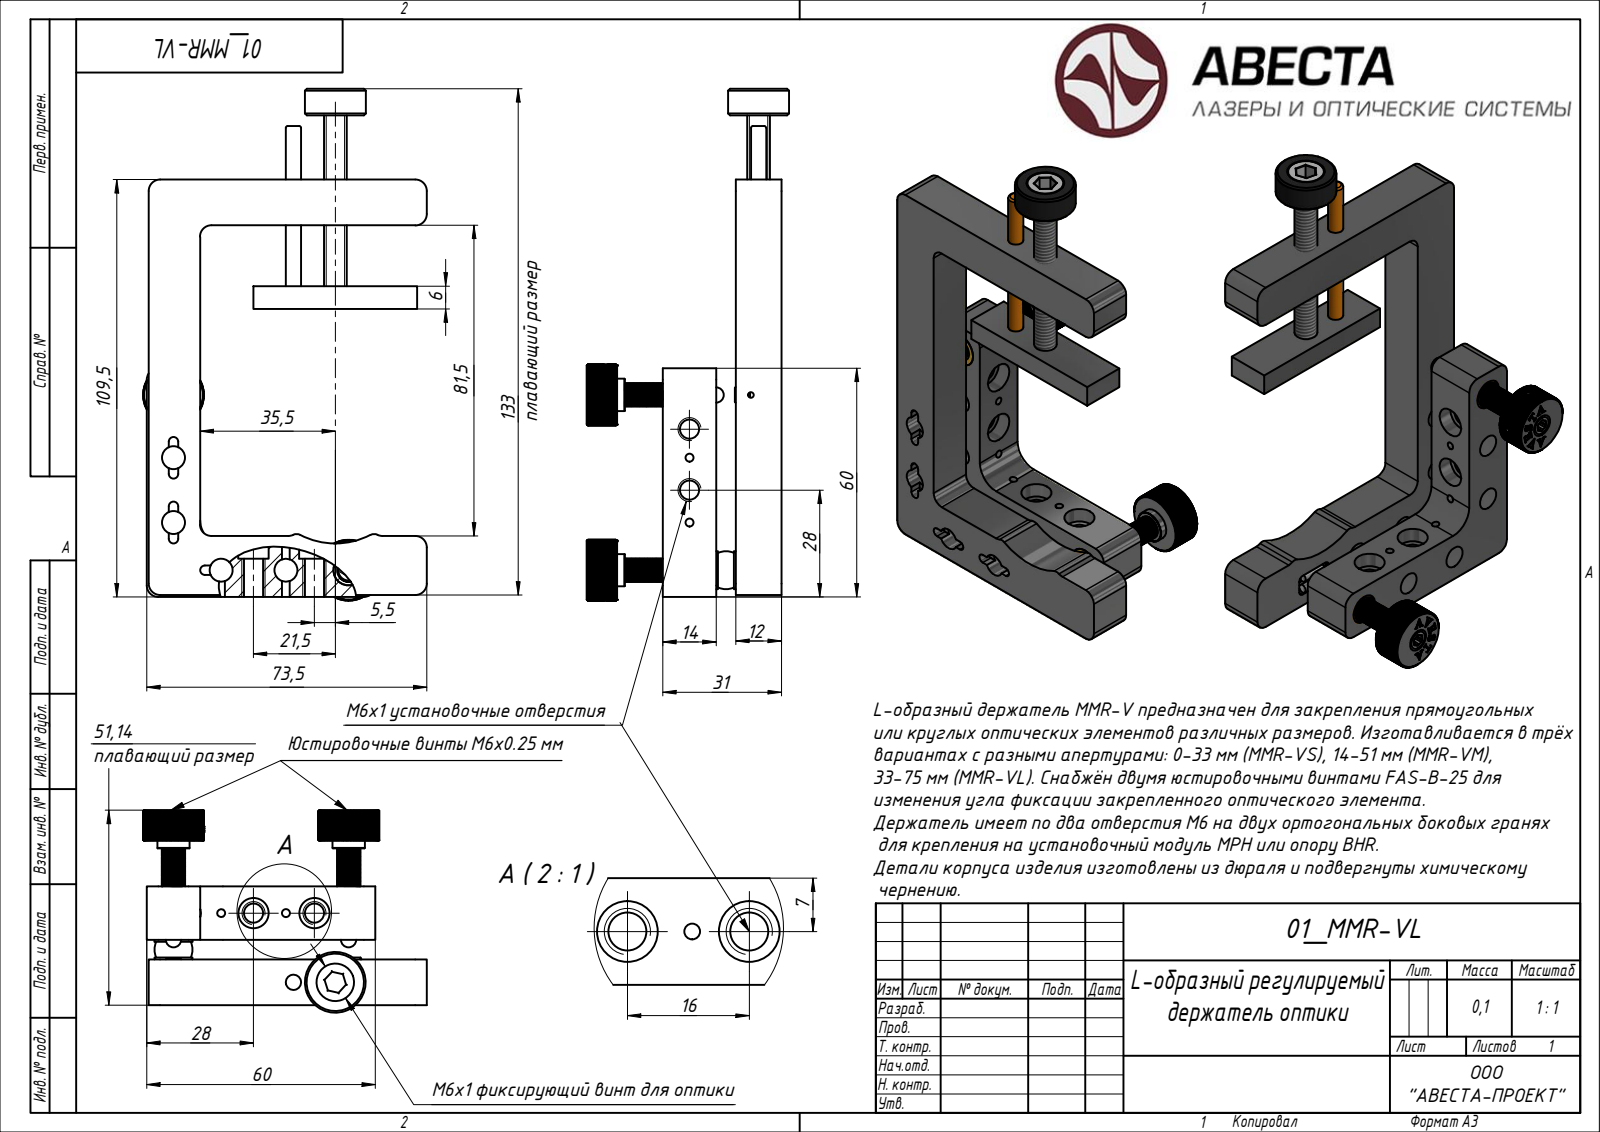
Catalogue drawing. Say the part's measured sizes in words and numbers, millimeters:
Its 3-D file was written by "ST-DEVELOPER v15 (AUTOMOTIVE_DESIGN)". It is 18 solids with 722 faces: 323 planar, 0 cylindrical and 399 other. Overall it measures 134.35 by 74.5 by 48.2 millimeters. Its volume is 62 704 cubic millimeters and its surface area 32 528 square millimeters. The main face-to-face distances are 12, 14, 13.5, 0.5, 19.14, 31.14, 5.14, 17.14, 109, 109.5.
